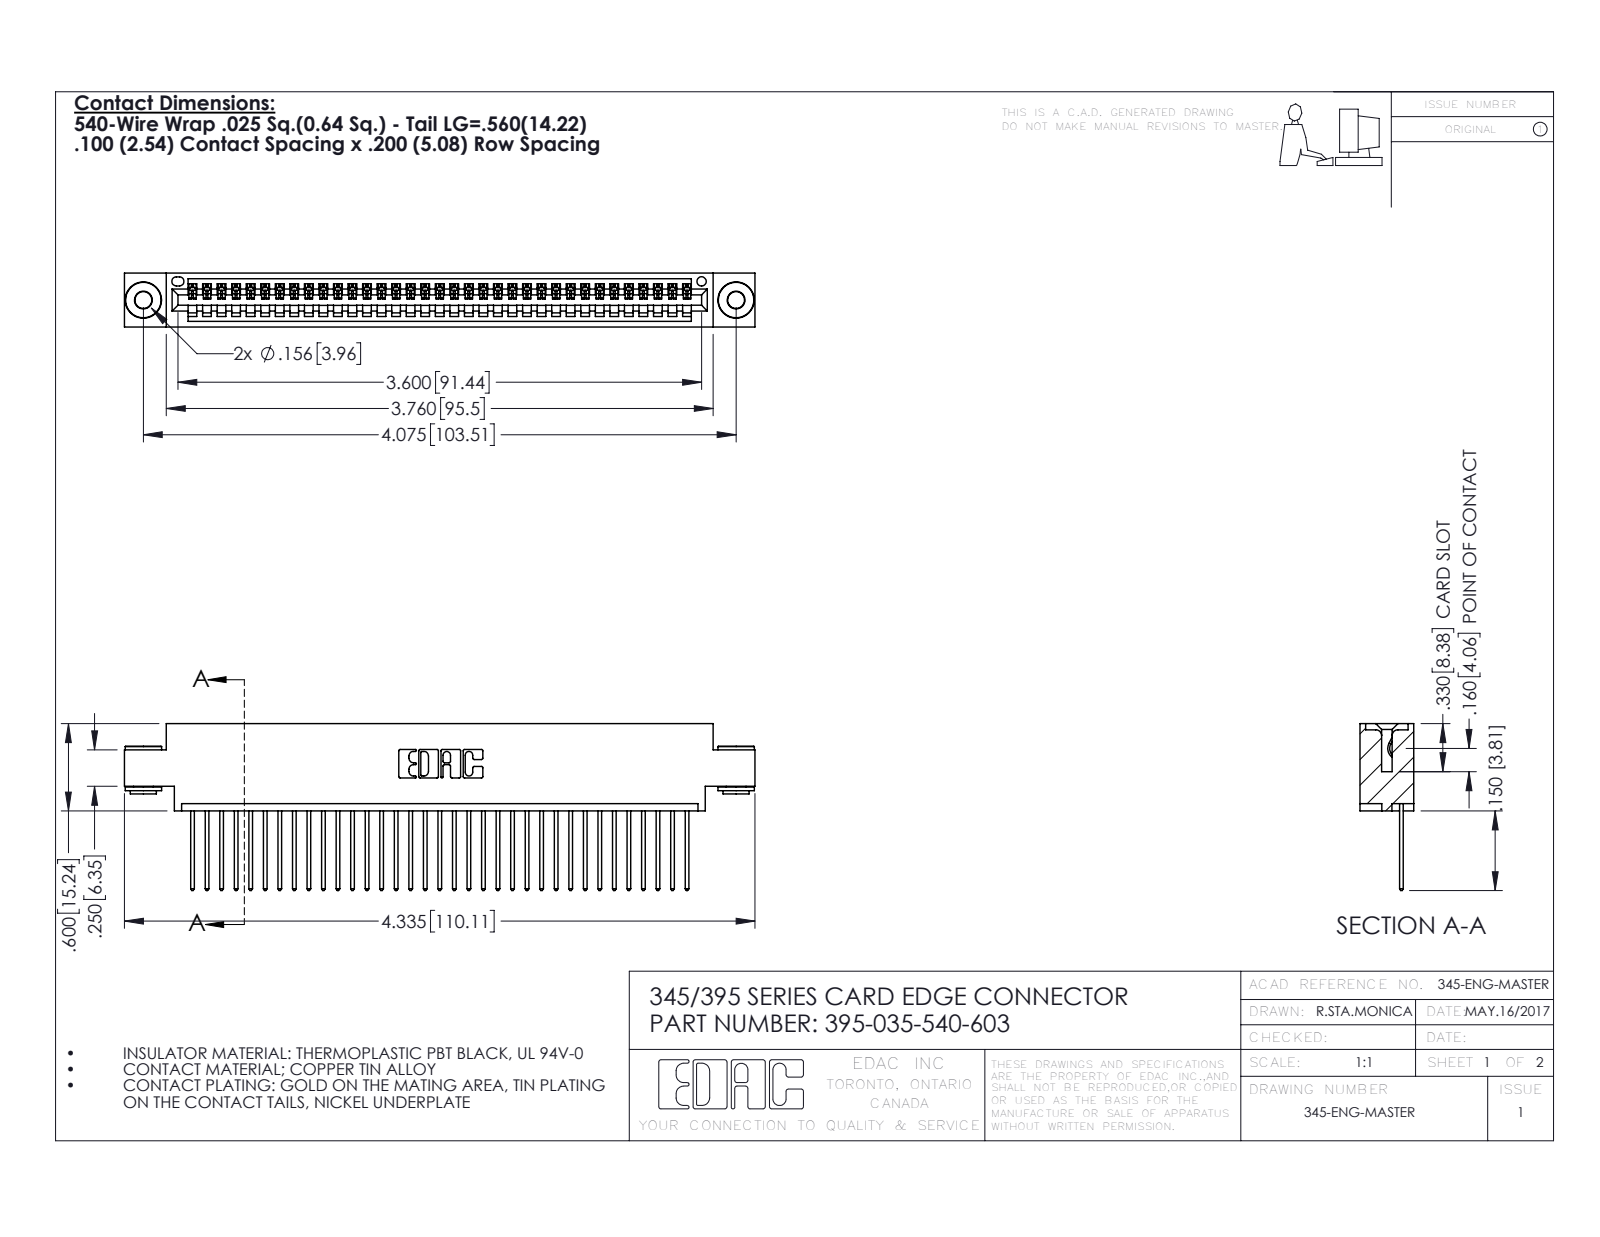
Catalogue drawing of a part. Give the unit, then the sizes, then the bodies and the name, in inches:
Units: inches
Overall size (bounding box): 4.335 × 1.147 × 0.37
Round holes (diameter × count): ⌀0.116 ×2, ⌀0.156 ×2, ⌀0.064 ×1
Round bosses / shafts (diameter × count): ⌀0.25 ×2, ⌀0.18 ×2, ⌀0.136 ×2
Partial cylindrical surfaces — rounded edges, fillets, slot ends (radius × count): R0.006 ×70, R0.01 ×70, R0.01 ×22, R0.007 ×6, R0.031 ×6, R0.026 ×3, R0.031 ×2, R0.04 ×2
Main face-to-face distances: 0.072, 0.298, 0.37, 0.098, 0.272, 0.025, 0.2, 0.225, 0.175, 0.149
Hole centre spacings: 0.27, 3.839, 4.075
Volume: 0.632 in³ · Surface area: 22.24 in²
Bodies: 38 solids, 2198 faces (1494 planar, 696 cylindrical, 8 other)
Part name (STEP PRODUCT): 345-250-002_345-250-002-102; 395-035-540-603; 345-292-001_345-293-140; 345 Part_0.170 Offset - 0.156 Dia-TH
STEP written by: SolidWorks 2016 (CONFIG_CONTROL_DESIGN)
